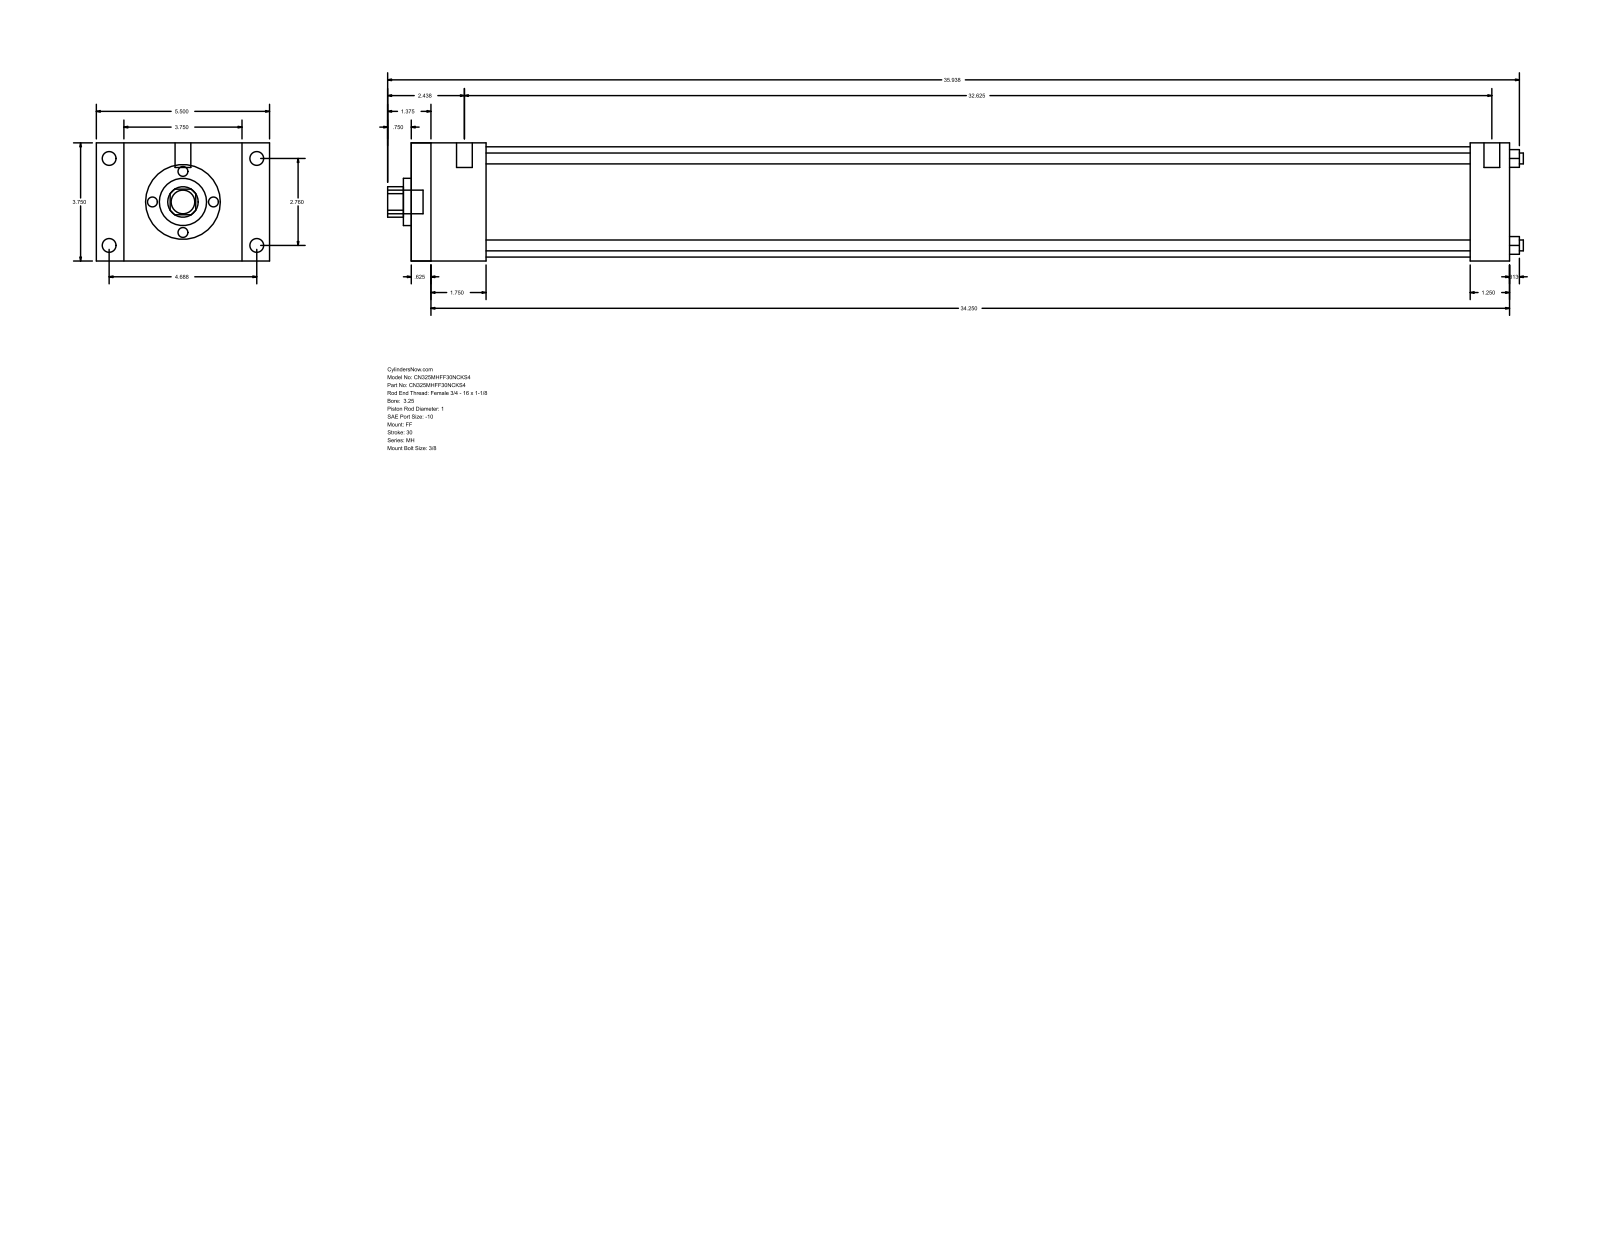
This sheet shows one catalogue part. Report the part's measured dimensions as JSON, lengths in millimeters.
{"part_name": "MH_FF__0325_1", "step_written_by": "GSSL Pune (CONFIG_CONTROL_DESIGN)", "units": "millimeters", "bodies": {"solids": 0, "faces": 92, "planar": 64, "cylindrical": 28, "other": 0}, "overall_size": [915.99, 139.7, 95.25], "round_holes": [[8.76, 4], [25.4, 1], [38.1, 1], [88.9, 1]], "round_bosses_or_shafts": [[11.13, 4], [5.56, 4], [12.7, 2], [19.05, 1]], "partial_cylinders_radius": [[12.29, 1]], "face_to_face_distances": [95.24, 885.83, 15.87, 869.96, 22.23, 117.47, 854.07, 838.2, 31.76, 60.33], "hole_center_spacings": [49.57, 70.1, 99.14]}
